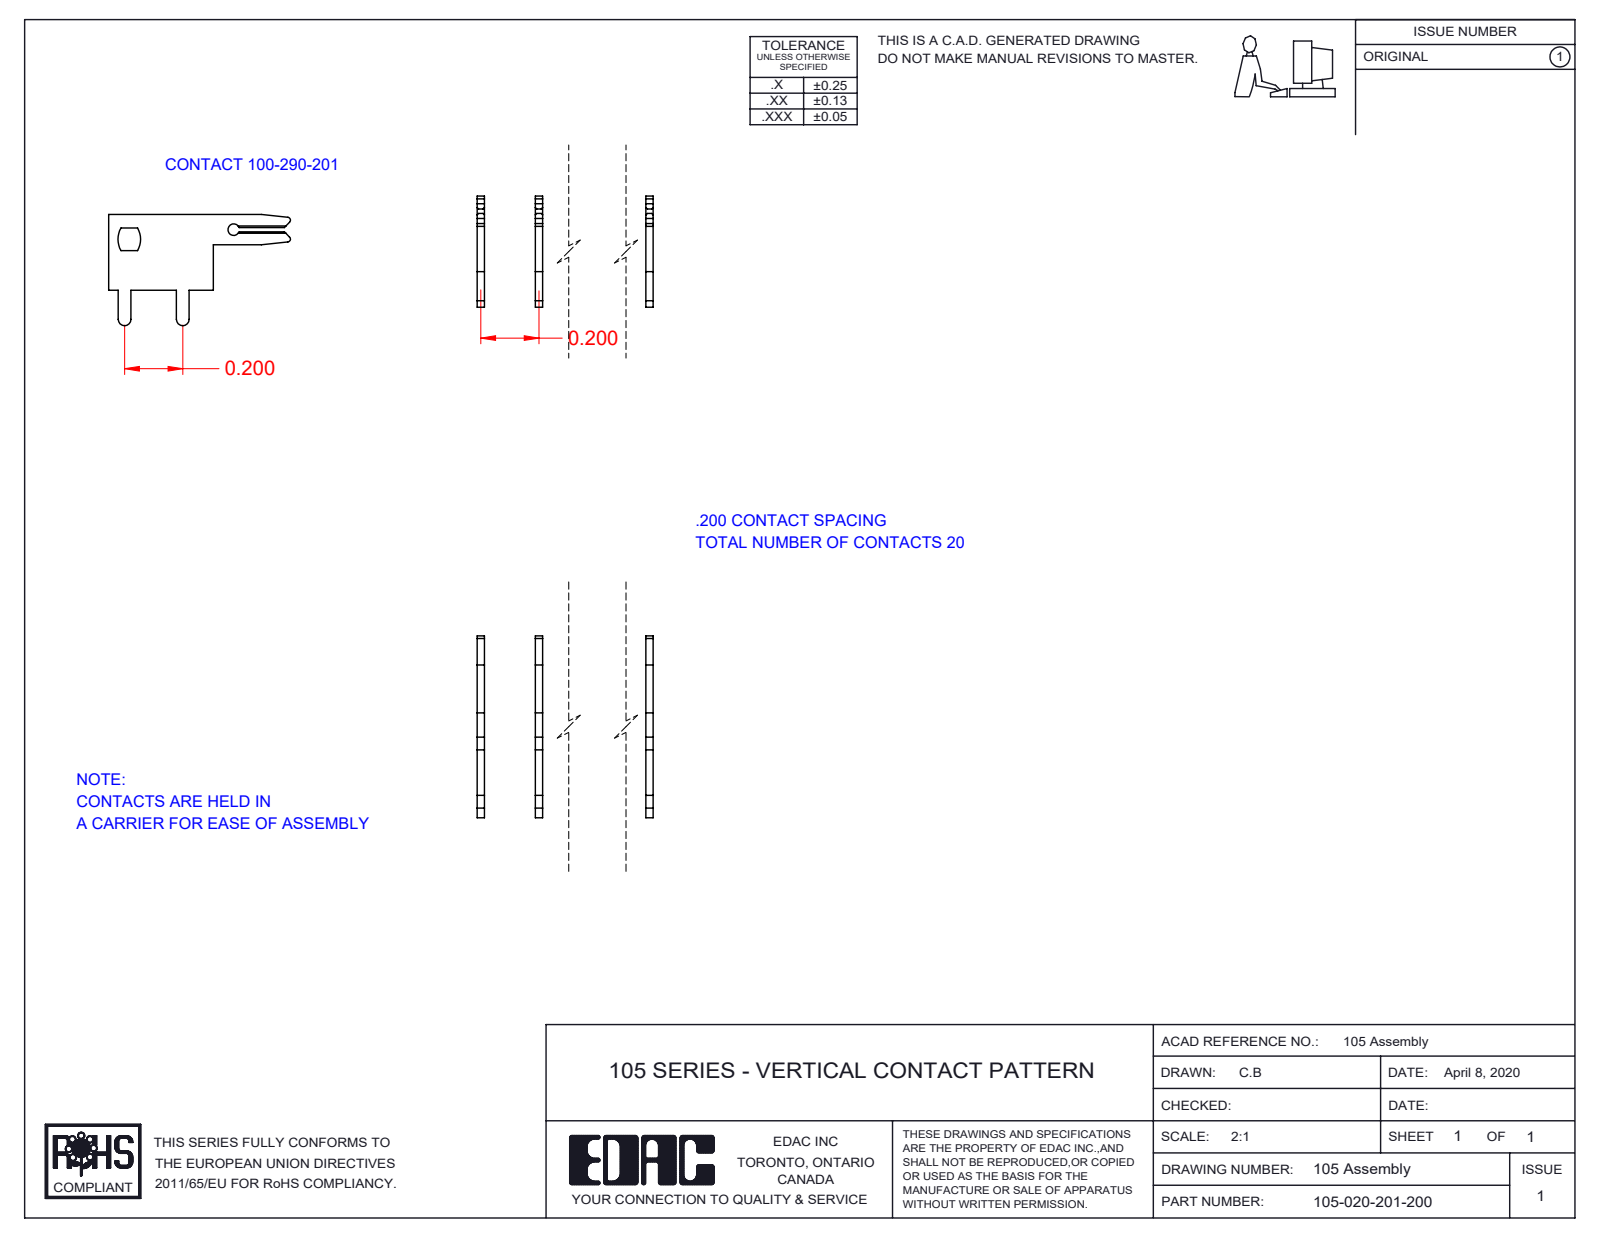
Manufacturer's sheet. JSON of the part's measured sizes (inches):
{"part_name": "100-290-001_100-290-201; 105-020-201-200", "step_written_by": "SolidWorks 2016 (CONFIG_CONTROL_DESIGN)", "units": "inches", "bodies": {"solids": 20, "faces": 700, "planar": 500, "cylindrical": 200, "other": 0}, "overall_size": [3.825, 0.625, 0.382], "volume_in3": 0.06, "surface_area_in2": 6.229, "round_holes": [[0.04, 1]], "partial_cylinders_radius": [[0.01, 2], [0.022, 2], [0.078, 2]], "face_to_face_distances": [0.2, 0.4, 0.6, 0.8, 1, 1.2, 1.4, 1.6, 1.8, 2]}
